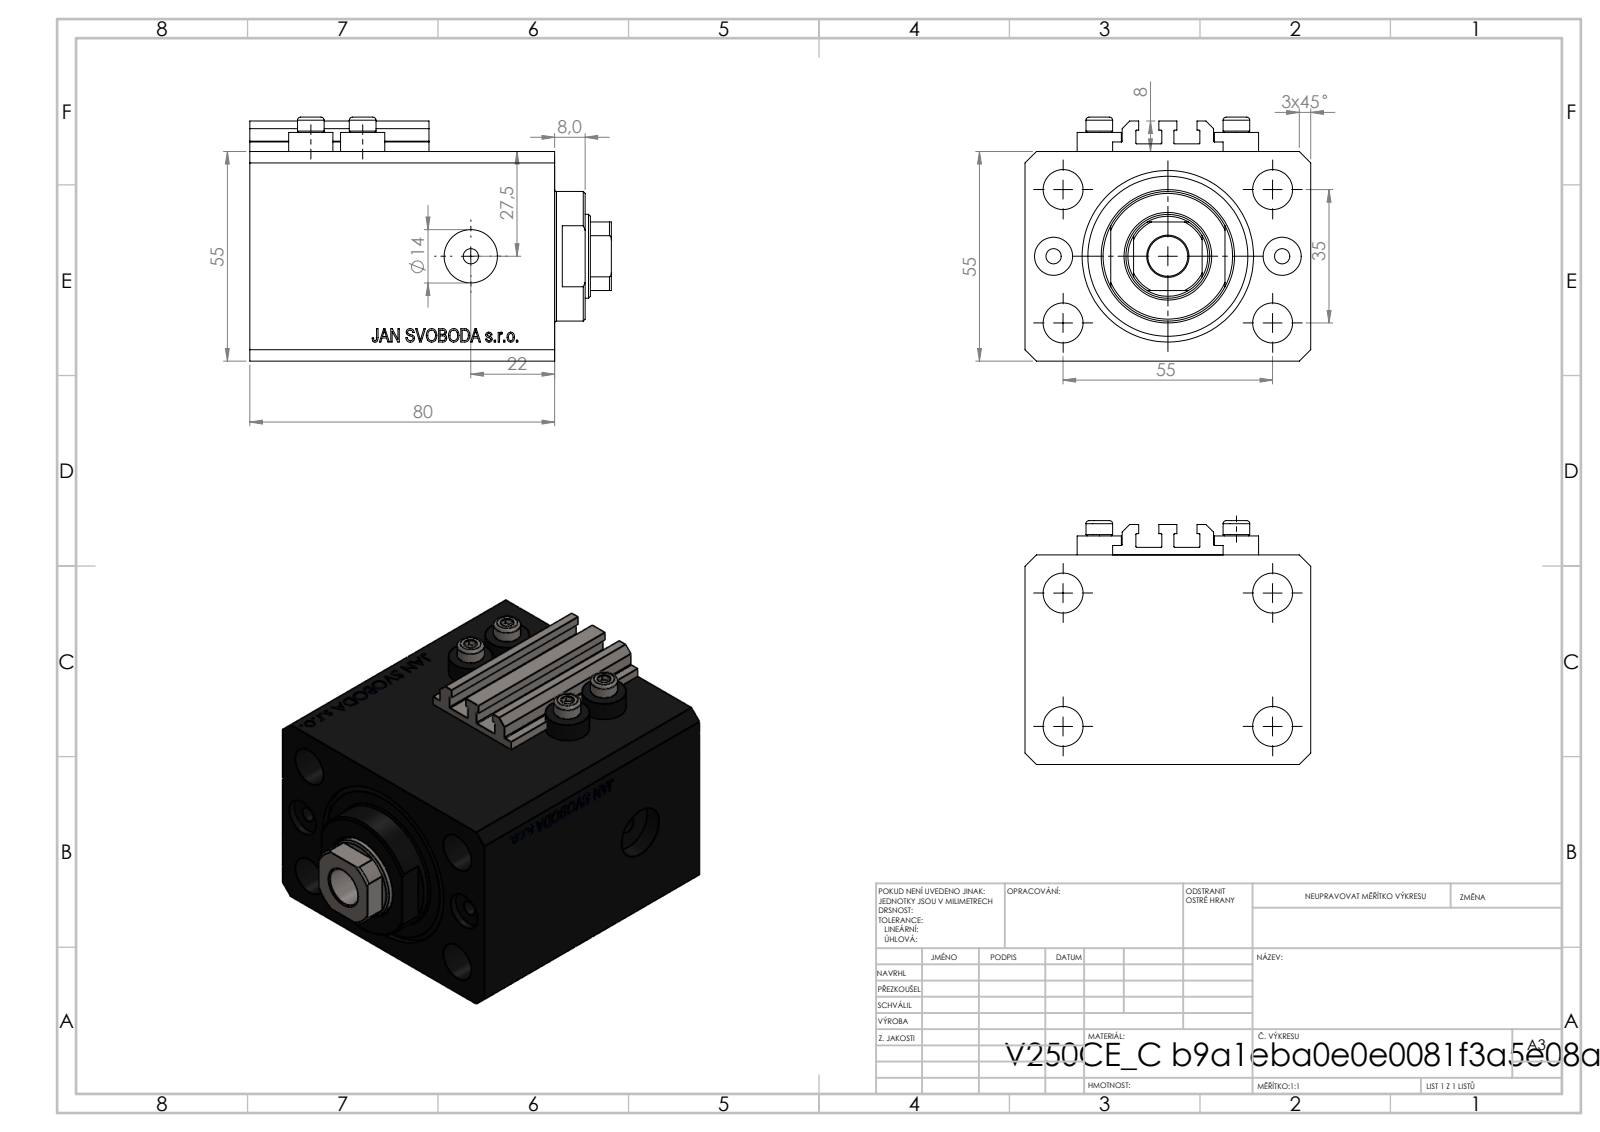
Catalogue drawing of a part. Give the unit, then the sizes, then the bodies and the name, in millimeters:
Units: millimetres
Overall size (bounding box): 94.9 × 75 × 64
Round holes (diameter × count): ⌀4 ×8, ⌀10.5 ×5, ⌀10 ×2, ⌀14 ×2, ⌀22 ×1, ⌀32 ×1, ⌀45 ×1
Round bosses / shafts (diameter × count): ⌀11.6 ×4, ⌀7 ×4, ⌀34 ×1
Partial cylindrical surfaces — rounded edges, fillets, slot ends (radius × count): R0.2 ×10, R10.5 ×1
Main face-to-face distances: 55, 75, 80, 27.1, 52.9, 9.9, 43, 70.1, 3, 8
Hole centre spacings: 17.68, 32.6, 60.1, 36, 13.6, 30, 35, 38.48
Volume: 304 987 mm³ · Surface area: 74 112 mm²
Bodies: 8 solids, 1033 faces (503 planar, 86 cylindrical, 444 other)
Part name (STEP PRODUCT): V250CE_VC_C; V250CE_C_VCP; ALLEN BOLT V250CE; V250CE_C_Body
STEP written by: SolidWorks 2019 (CONFIG_CONTROL_DESIGN)
